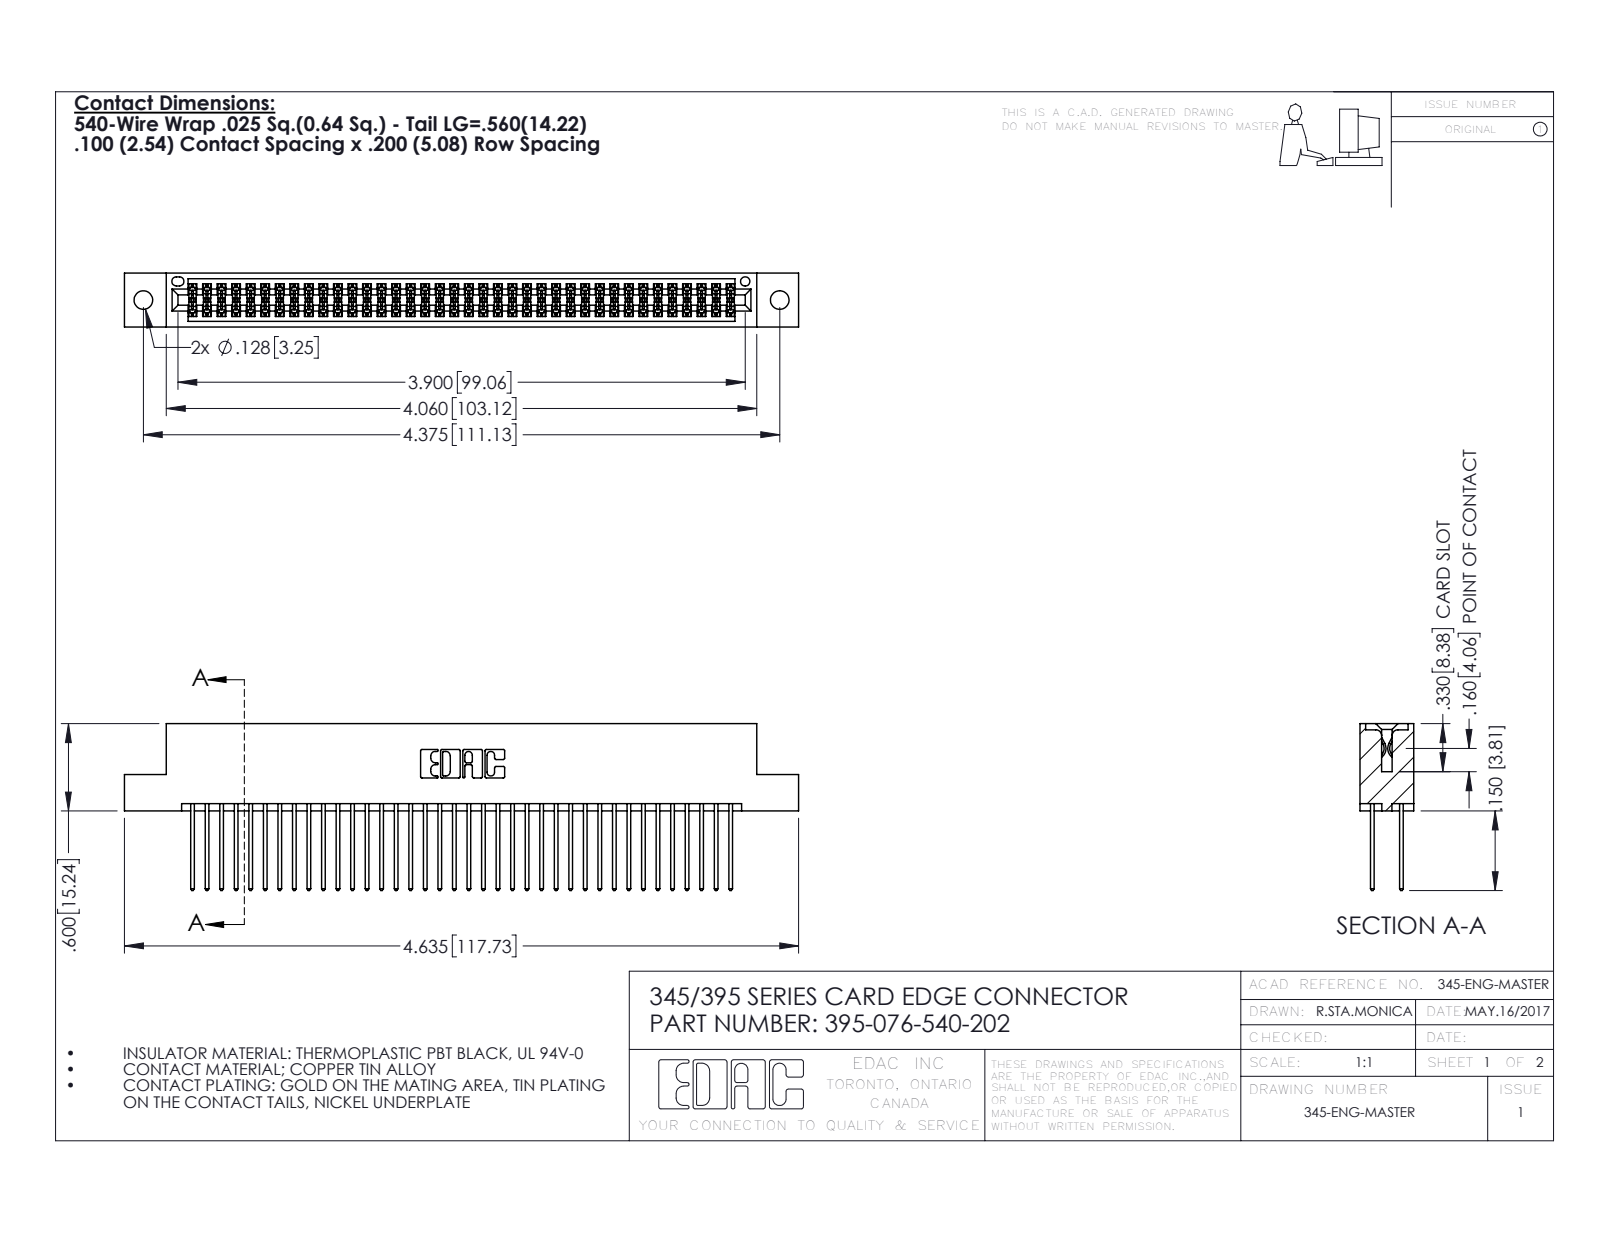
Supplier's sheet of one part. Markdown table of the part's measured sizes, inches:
| quantity | value |
| --- | --- |
| part name | 395-076-540-202; 345-292-001_345-293-140; 345 Part_Flush Mounting Lugs - 0.128 Dia |
| STEP written by | SolidWorks 2016 (CONFIG_CONTROL_DESIGN) |
| units | inches |
| bodies | 77 solids, 3926 faces (2588 planar, 1338 cylindrical, 0 other) |
| overall size | 4.635 × 1.147 × 0.37 |
| volume | 0.711 in³ |
| surface area | 28.22 in² |
| round holes (diameter × count) | 0.128 × 2, 0.064 × 1 |
| partial cylindrical surfaces (radius × count) | 0.006 × 114, 0.01 × 76, 0.01 × 22, 0.007 × 6, 0.031 × 6, 0.026 × 3, 0.014 × 2, 0.019 × 2 |
| main face-to-face distances | 0.298, 0.072, 0.2, 0.098, 0.272, 0.025, 0.37, 0.225, 0.175, 0.149 |
| hole center spacings | 0.27, 4.139, 4.375 |
